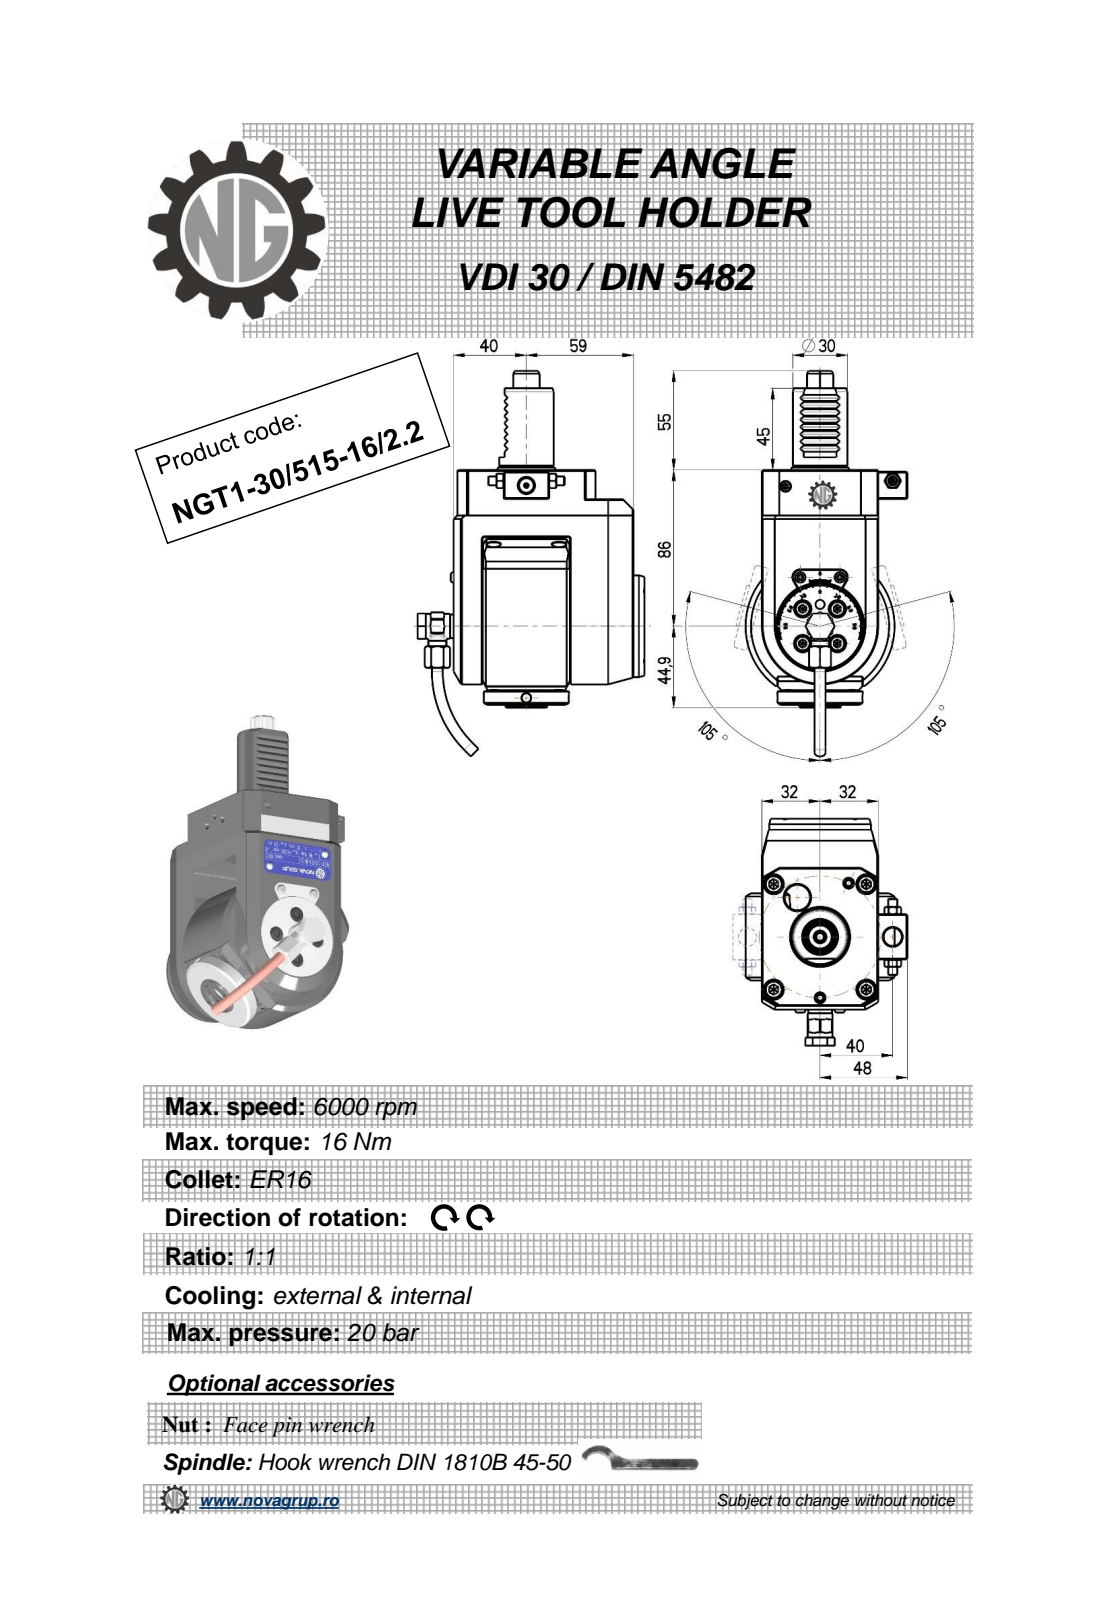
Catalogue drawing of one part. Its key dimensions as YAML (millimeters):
part_name: "NGT1_30_511_16_2_2"
step_written_by: "PRO/ENGINEER BY PARAMETRIC TECHNOLOGY CORPORATION, 2010280 (CONFIG_CONTROL_DESIGN)"
units: millimeters
bodies: {solids: 1, faces: 528, planar: 199, cylindrical: 166, other: 163}
overall_size: [212.67, 124.9, 89]
volume: 769717
surface_area: 70582
round_holes:
  - {diameter: 3.2, count: 4}
  - {diameter: 4, count: 3}
  - {diameter: 4.2, count: 2}
  - {diameter: 5, count: 2}
  - {diameter: 10, count: 2}
  - {diameter: 3, count: 1}
  - {diameter: 5.3, count: 1}
  - {diameter: 6.2, count: 1}
  - {diameter: 9, count: 1}
  - {diameter: 9.5, count: 1}
  - {diameter: 11, count: 1}
  - {diameter: 12.5, count: 1}
round_bosses_or_shafts:
  - {diameter: 6, count: 2}
  - {diameter: 5.7, count: 2}
  - {diameter: 56, count: 1}
  - {diameter: 47, count: 1}
  - {diameter: 35, count: 1}
  - {diameter: 30, count: 1}
  - {diameter: 23, count: 1}
  - {diameter: 13.6, count: 1}
partial_cylinders:
  - {radius: 2.91, count: 16}
  - {radius: 0.26, count: 12}
  - {radius: 0.3, count: 8}
  - {radius: 0.16, count: 6}
  - {radius: 0.5, count: 4}
  - {radius: 1, count: 2}
  - {radius: 5.75, count: 1}
  - {radius: 7.25, count: 1}
face_to_face_distances: [64, 16, 37, 99, 6, 105, 21, 14, 62, 35]
hole_center_spacings: [9.25, 13.08, 18.5, 41.06, 49.87, 50.26, 0.4, 30.75]
